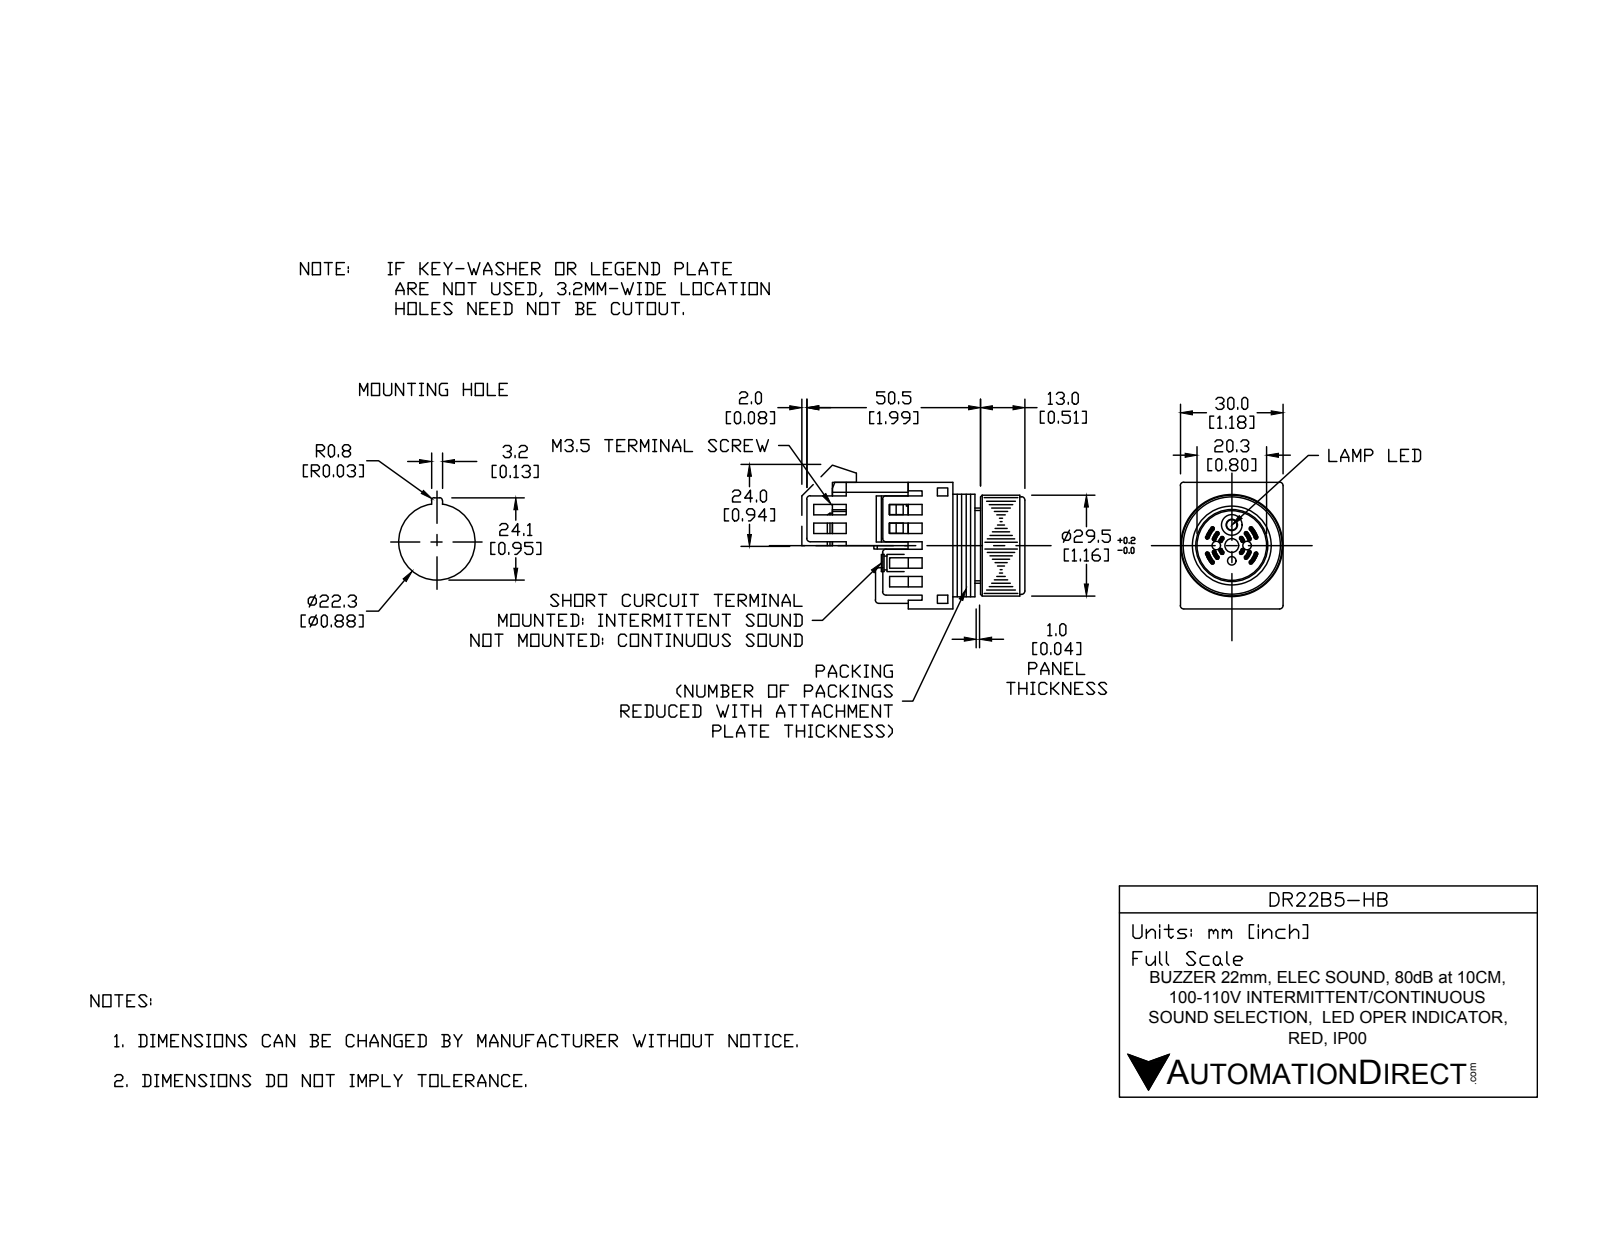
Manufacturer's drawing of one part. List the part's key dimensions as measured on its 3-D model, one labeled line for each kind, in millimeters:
Part name (STEP PRODUCT): DR22B5-HB
STEP written by: SolidWorks 2017 (AUTOMOTIVE_DESIGN)
Units: millimetres
Bodies: 13 solids, 196 faces (113 planar, 71 cylindrical, 12 other)
Overall size (bounding box): 63.5 × 42 × 30.8
Volume: 39 666 mm³ · Surface area: 19 942 mm²
Round holes (diameter × count): ⌀2.2 ×3, ⌀7 ×2, ⌀2.5 ×1, ⌀4 ×1, ⌀20.8 ×1, ⌀22.5 ×1
Round bosses / shafts (diameter × count): ⌀5 ×2, ⌀30.8 ×1, ⌀29.5 ×1, ⌀22 ×1, ⌀20.2 ×1
Partial cylindrical surfaces — rounded edges, fillets, slot ends (radius × count): R0.5 ×10, R2 ×2, R4.5 ×2
Main face-to-face distances: 1.5, 3, 1.25, 4.5, 2.75, 1.75, 30, 18.5, 13, 4.25
Hole centre spacings: 4.5, 6.36, 7.11, 15.69, 18.34, 19.7, 21.91, 24.82
